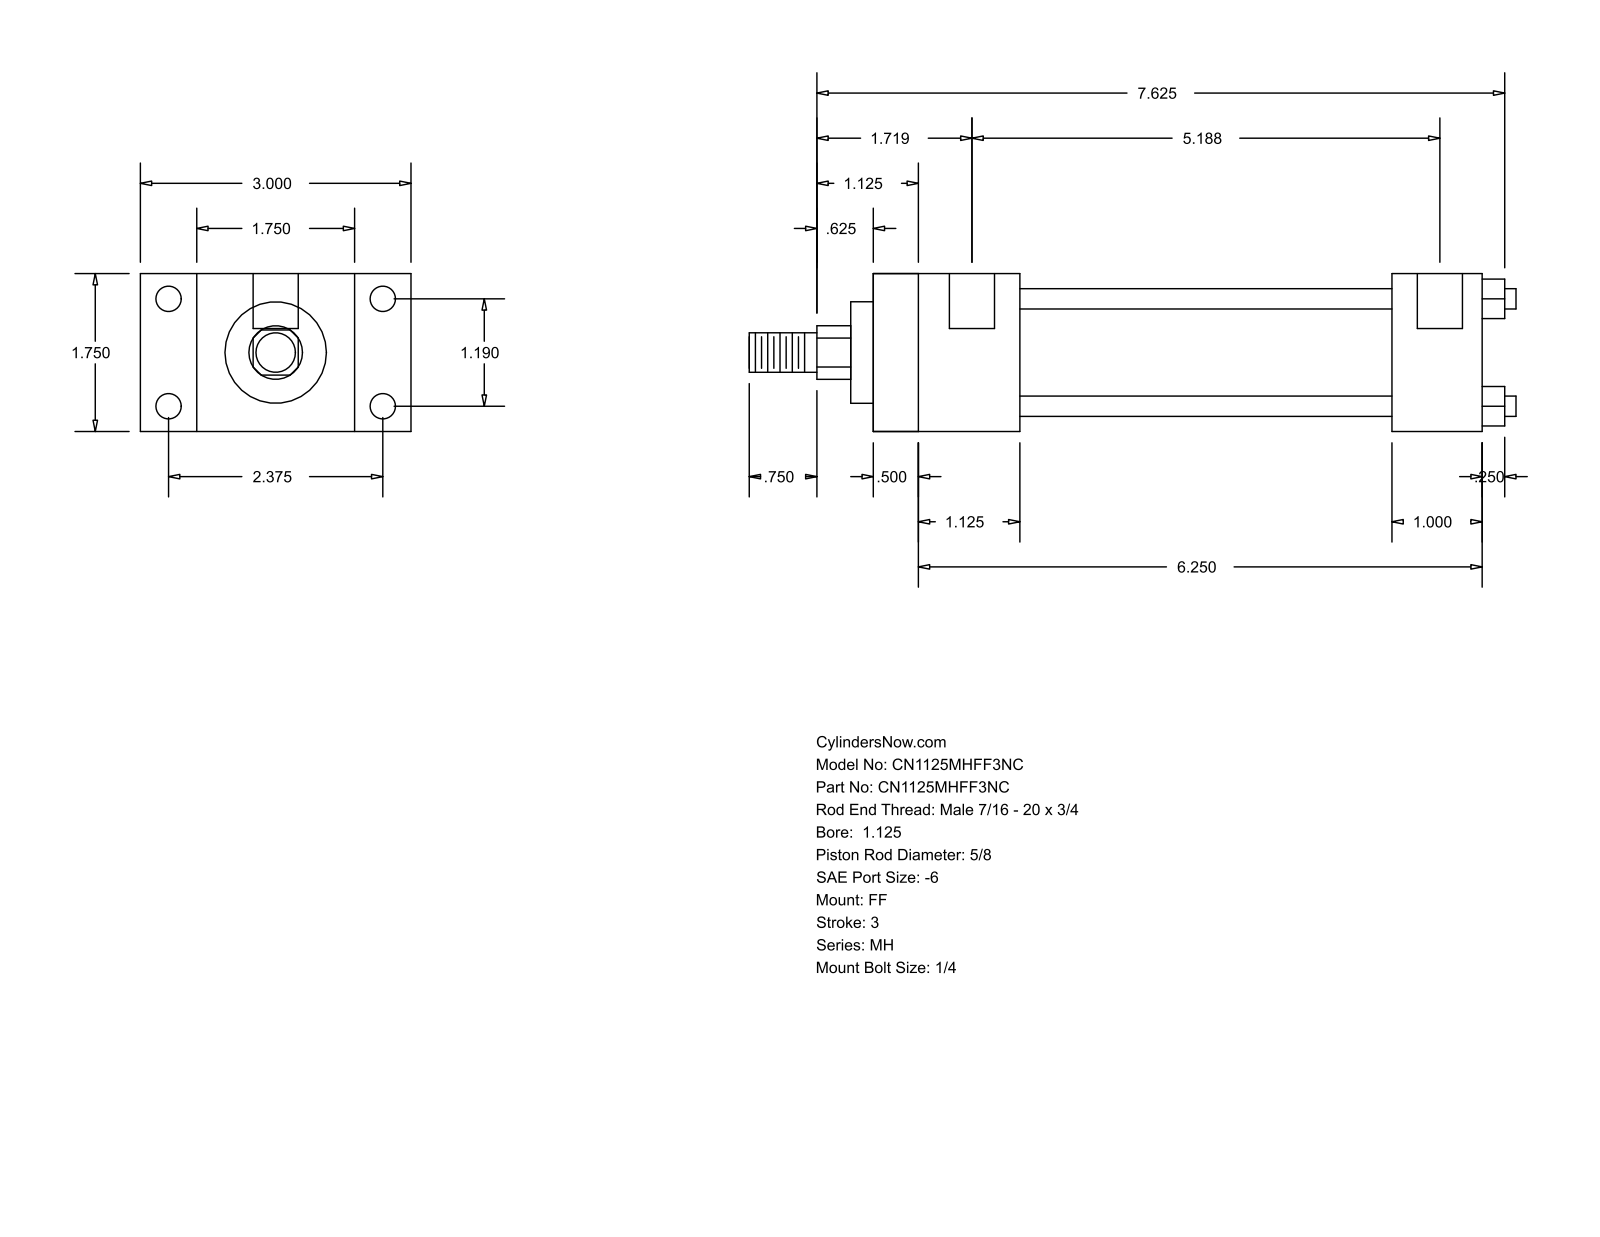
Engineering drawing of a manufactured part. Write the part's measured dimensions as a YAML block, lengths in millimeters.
part_name: "MH_FF__0112_0.625"
step_written_by: "GSSL Pune (CONFIG_CONTROL_DESIGN)"
units: millimeters
bodies: {solids: 0, faces: 92, planar: 64, cylindrical: 28, other: 0}
overall_size: [215.9, 76.2, 44.45]
round_holes:
  - {diameter: 5.56, count: 4}
  - {diameter: 7.14, count: 4}
  - {diameter: 12.7, count: 2}
round_bosses_or_shafts:
  - {diameter: 5.71, count: 4}
  - {diameter: 34.92, count: 1}
  - {diameter: 28.57, count: 1}
  - {diameter: 15.88, count: 1}
  - {diameter: 11.11, count: 1}
partial_cylinders:
  - {radius: 7.54, count: 1}
face_to_face_distances: [44.46, 171.44, 15.87, 12.69, 158.75, 28.58, 60.33, 41.27, 146.05, 133.36]
hole_center_spacings: [30.22, 60.32, 67.47, 128.59, 3.17, 131.76]
